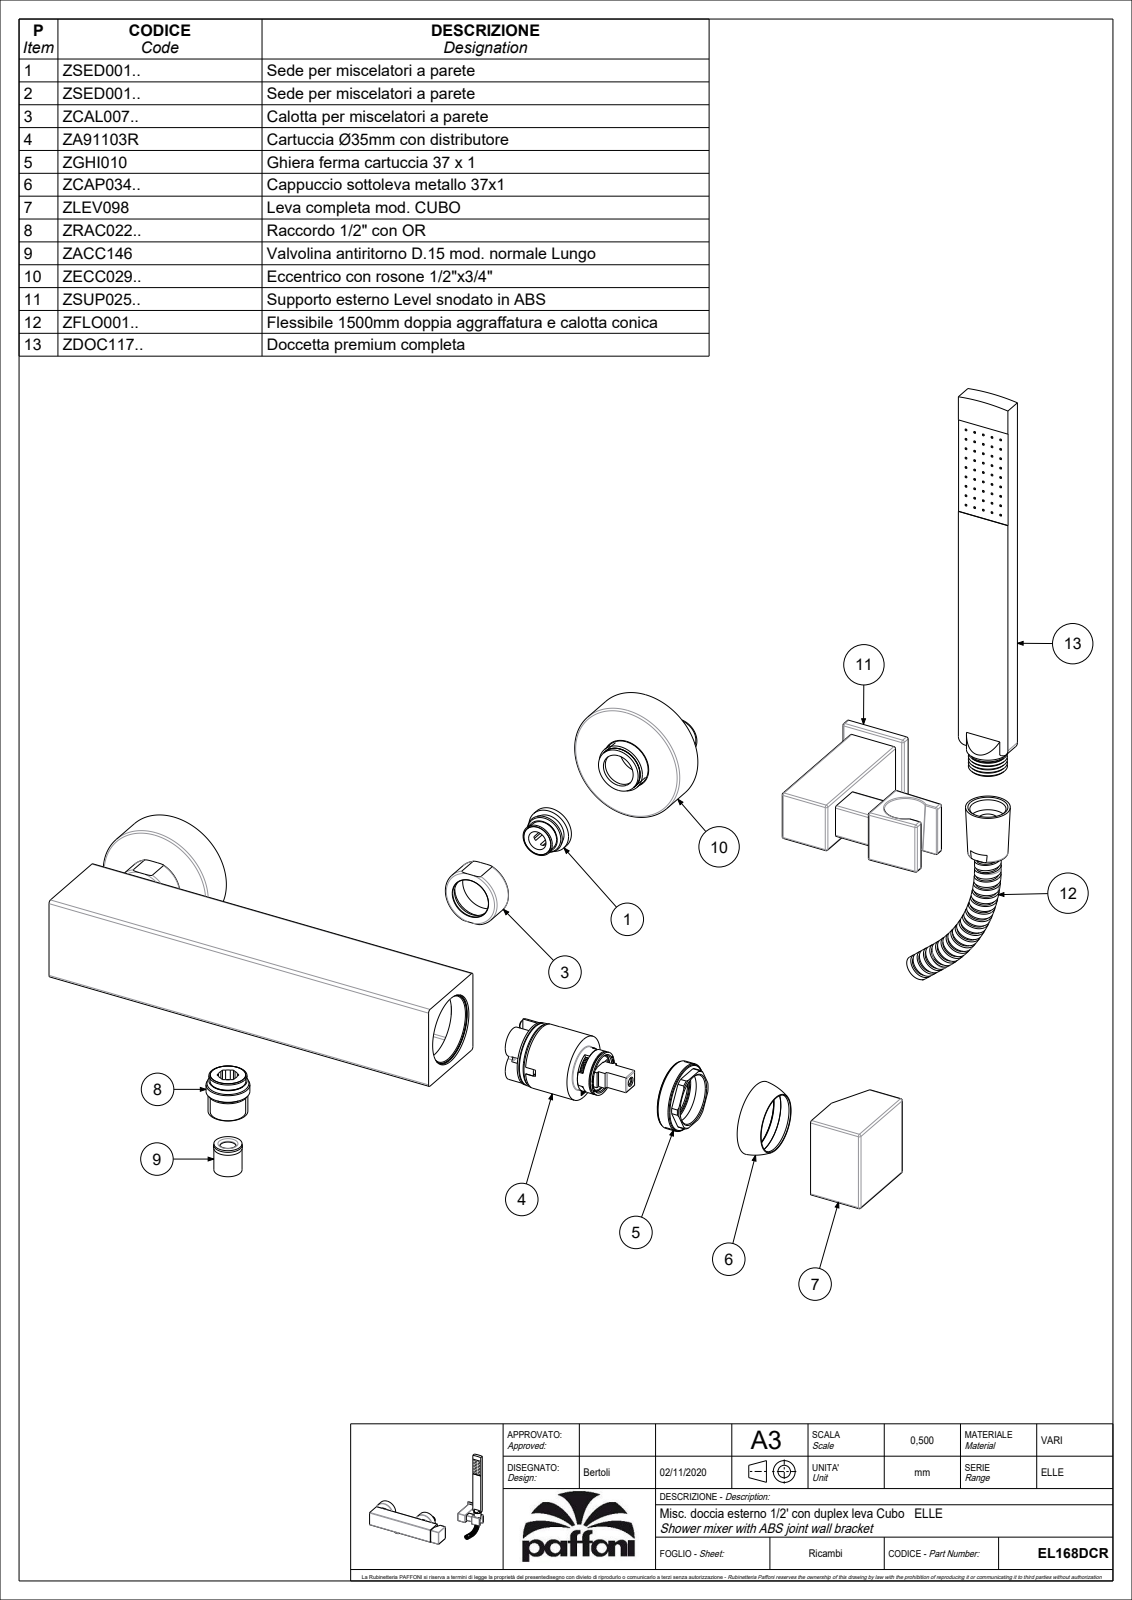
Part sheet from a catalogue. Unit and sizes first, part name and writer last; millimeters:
Units: millimetres
Overall size (bounding box): 475.25 × 371 × 81.5
Round holes (diameter × count): ⌀21.6 ×2, ⌀24.5 ×2, ⌀25 ×2, ⌀62.3 ×2, ⌀42 ×1
Round bosses / shafts (diameter × count): ⌀63.5 ×2, ⌀27 ×2, ⌀22.5 ×1, ⌀20.9 ×1, ⌀18 ×1, ⌀15 ×1, ⌀9 ×1, ⌀8 ×1
Partial cylindrical surfaces — rounded edges, fillets, slot ends (radius × count): R1 ×40, R0.5 ×6, R1.5 ×4, R4 ×2, R15.6 ×2, R3 ×1, R3.95 ×1, R113 ×1
Main face-to-face distances: 46.5, 35, 81.5, 27.75, 53.75, 18.75, 34.97, 53.72, 81.47, 15
Hole centre spacings: 150
Volume: 718 199 mm³ · Surface area: 151 580 mm²
Bodies: 4 solids, 323 faces (90 planar, 103 cylindrical, 130 other)
Part name (STEP PRODUCT): EL168DCR
STEP written by: CREO PARAMETRIC BY PTC INC, 2020044 (CONFIG_CONTROL_DESIGN)
